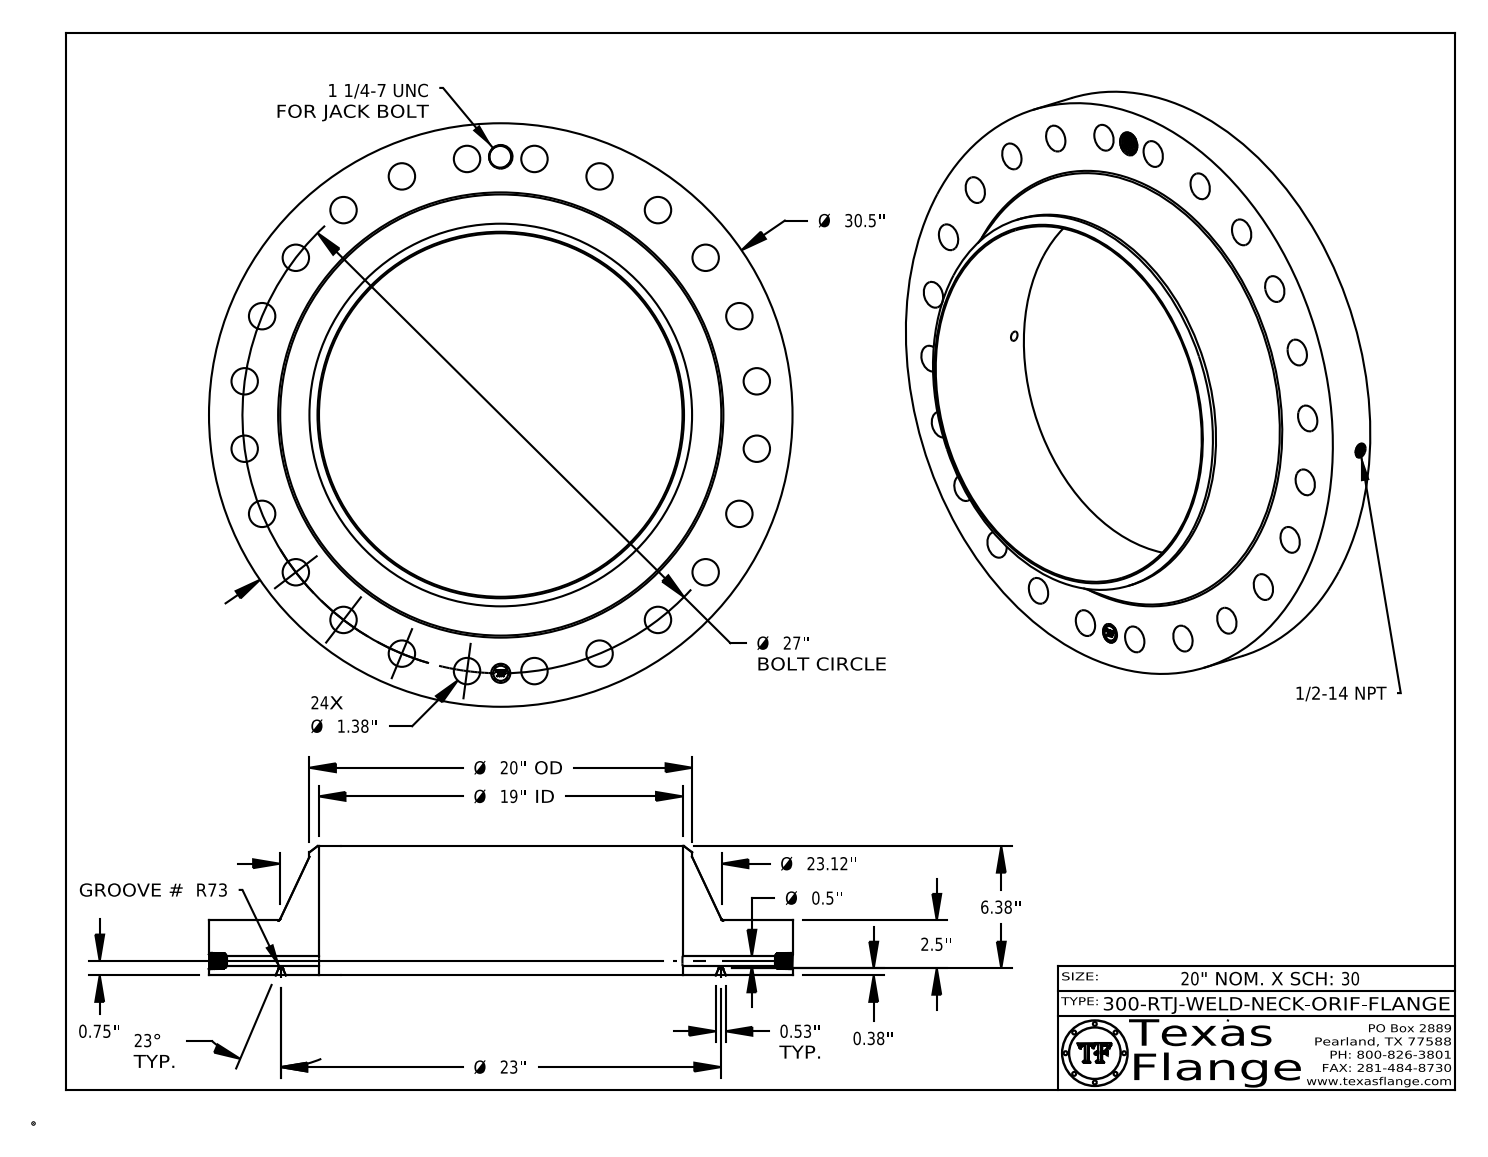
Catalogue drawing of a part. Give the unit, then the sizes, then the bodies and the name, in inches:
Units: inches
Overall size (bounding box): 30.5 × 30.5 × 6.755
Round holes (diameter × count): ⌀1.38 ×24, ⌀0.5 ×1, ⌀0.672 ×1, ⌀1 ×1, ⌀1.109 ×1, ⌀19 ×1
Round bosses / shafts (diameter × count): ⌀0.061 ×8, ⌀30.5 ×1, ⌀20 ×1, ⌀0.788 ×1
Main face-to-face distances: 2.875, 0.375, 2.5, 6.755, 6.38, 3.88, 0.015, 2.86, 2.485, 3.895
Hole centre spacings: 13.5, 23.383, 24.945, 21.42, 3.524, 6.988, 19.092, 26.08
Volume: 1 452 in³ · Surface area: 2 032 in²
Bodies: 1 solid, 840 faces (370 planar, 134 cylindrical, 336 other)
Part name (STEP PRODUCT): 300-RTJ-WELD-NECK
STEP written by: CATIA V5 STEP AP214 (AUTOMOTIVE_DESIGN)
